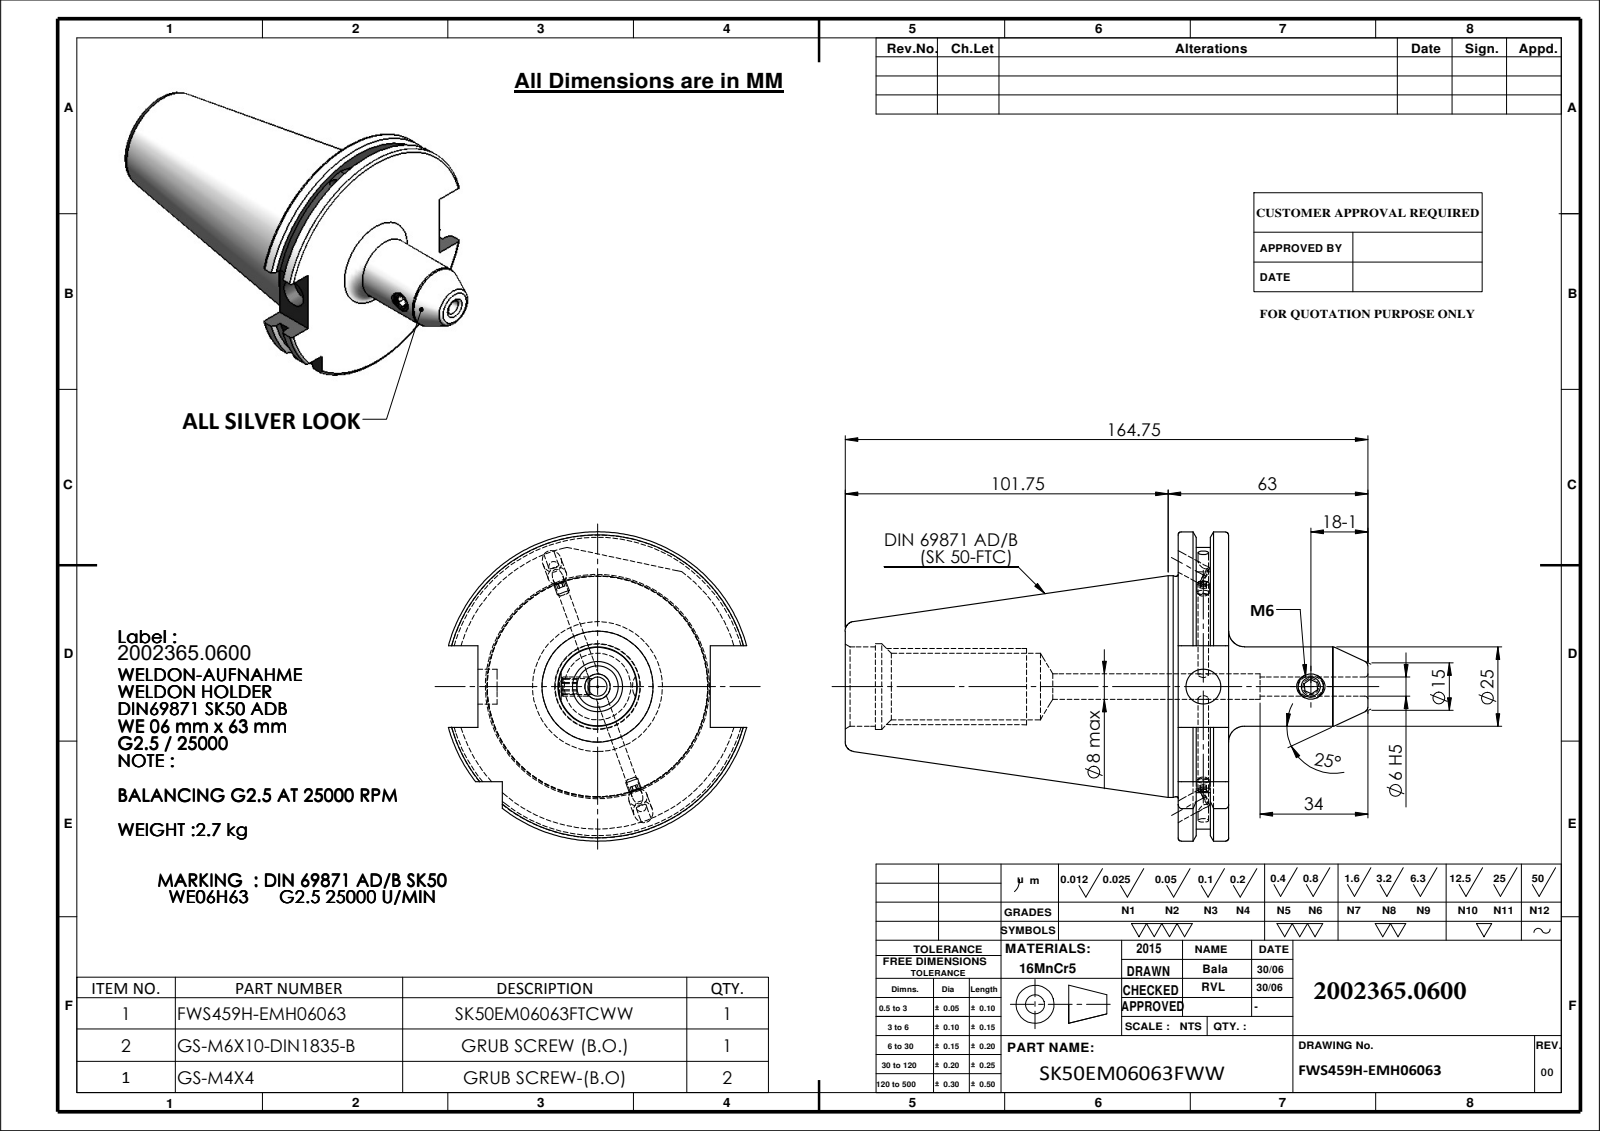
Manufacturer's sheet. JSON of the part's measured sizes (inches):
{"part_name": "SK50EM06063FTCWW; M6X10._DIN 913 - M8 x 8-N; Copy of M4X4_DIN 913 - M4 x 4-N; 91506-WE706063", "step_written_by": "SolidWorks 2009 (CONFIG_CONTROL_DESIGN)", "units": "inches", "bodies": {"solids": 4, "faces": 164, "planar": 51, "cylindrical": 53, "other": 60}, "overall_size": [6.486, 3.839, 3.703], "volume_in3": 21.57, "surface_area_in2": 73.5, "round_holes": [[0.236, 3], [0.315, 2], [0.13, 1], [0.197, 1], [0.433, 1], [0.827, 1], [0.984, 1], [1.063, 1]], "round_bosses_or_shafts": [[0.157, 2], [2.75, 1], [2.734, 1], [0.236, 1]], "partial_cylinders_radius": [[1.768, 1], [1.919, 1]], "face_to_face_distances": [0.626, 0.223, 0.403, 0.4, 0.177, 0.226, 4.132, 4.355, 4.531, 4.758], "hole_center_spacings": [1.335]}
